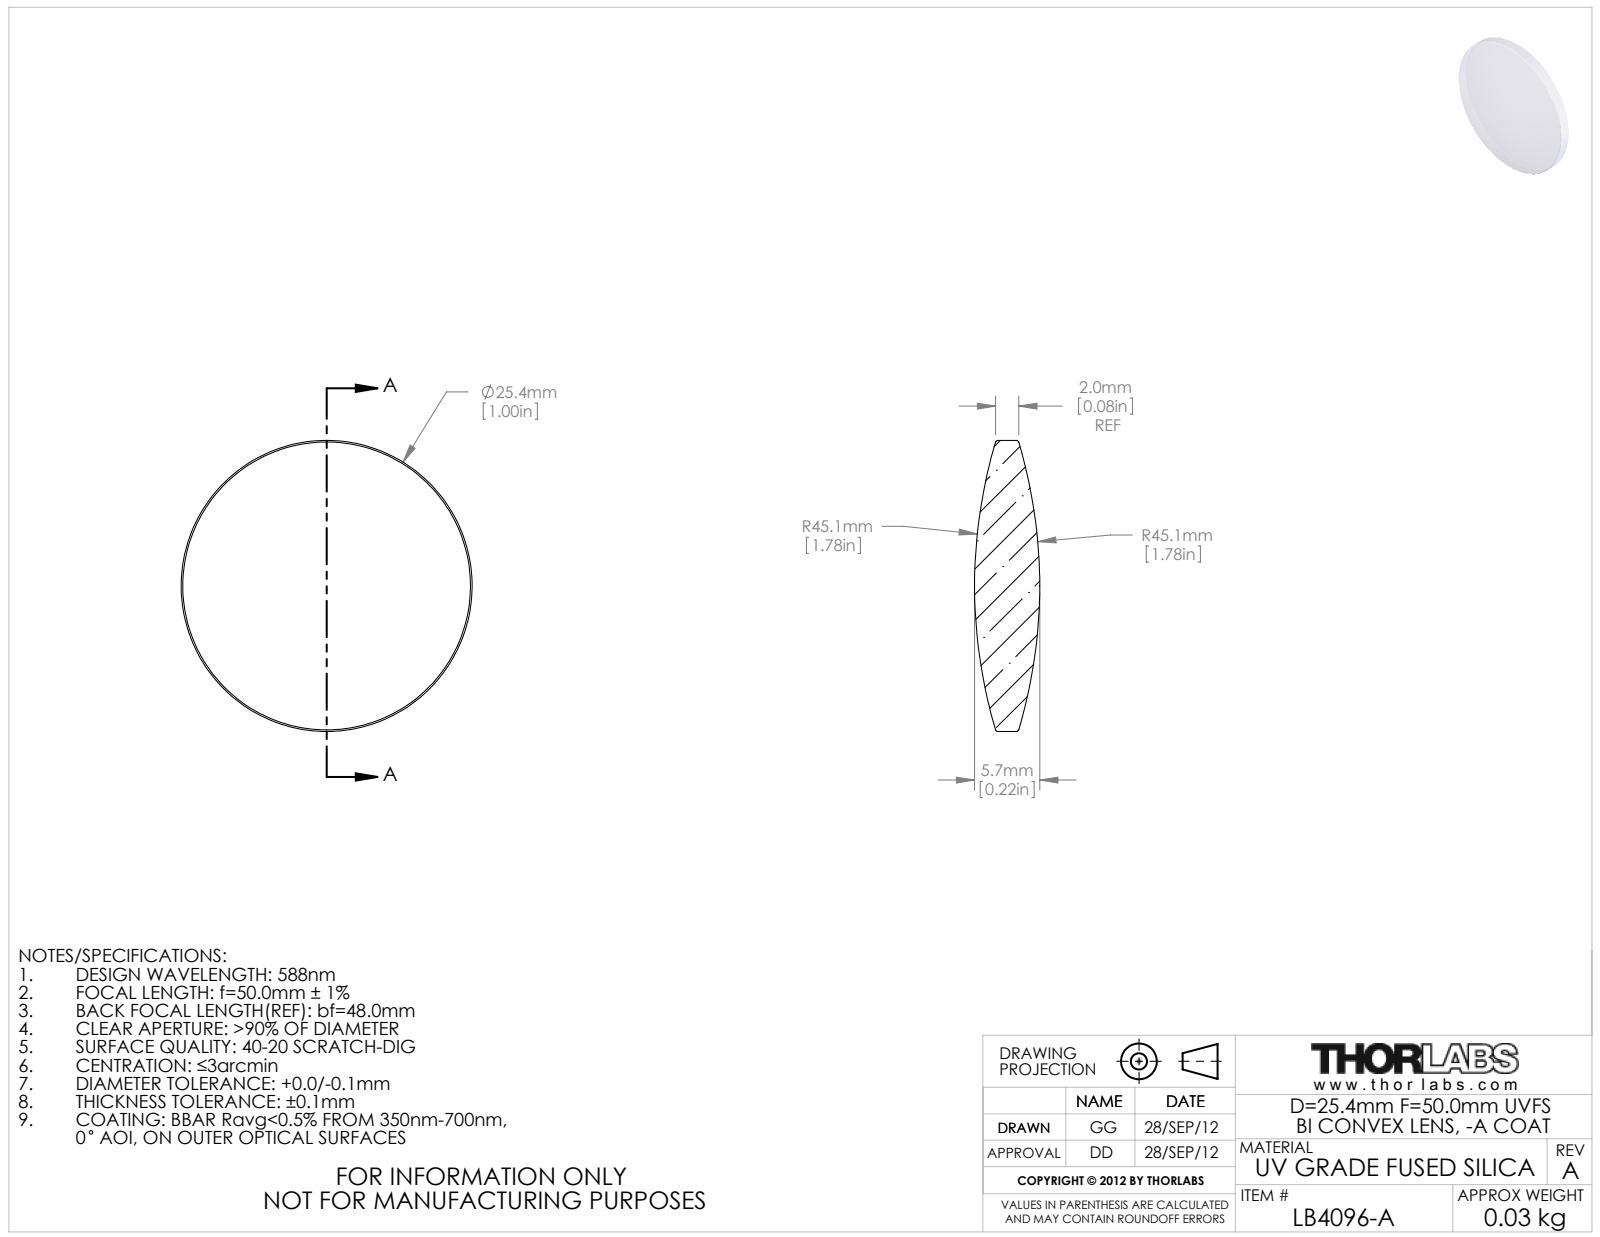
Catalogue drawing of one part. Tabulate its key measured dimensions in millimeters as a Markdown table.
| quantity | value |
| --- | --- |
| part name | 25011-E0W |
| STEP written by | SolidWorks 2011 (CONFIG_CONTROL_DESIGN) |
| units | millimeters |
| bodies | 1 solid, 10 faces (0 planar, 2 cylindrical, 8 other) |
| overall size | 25.4 × 25.4 × 5.7 |
| volume | 1 935 mm³ |
| surface area | 1 183 mm² |
| round bosses / shafts (diameter × count) | 25.4 × 1 |
